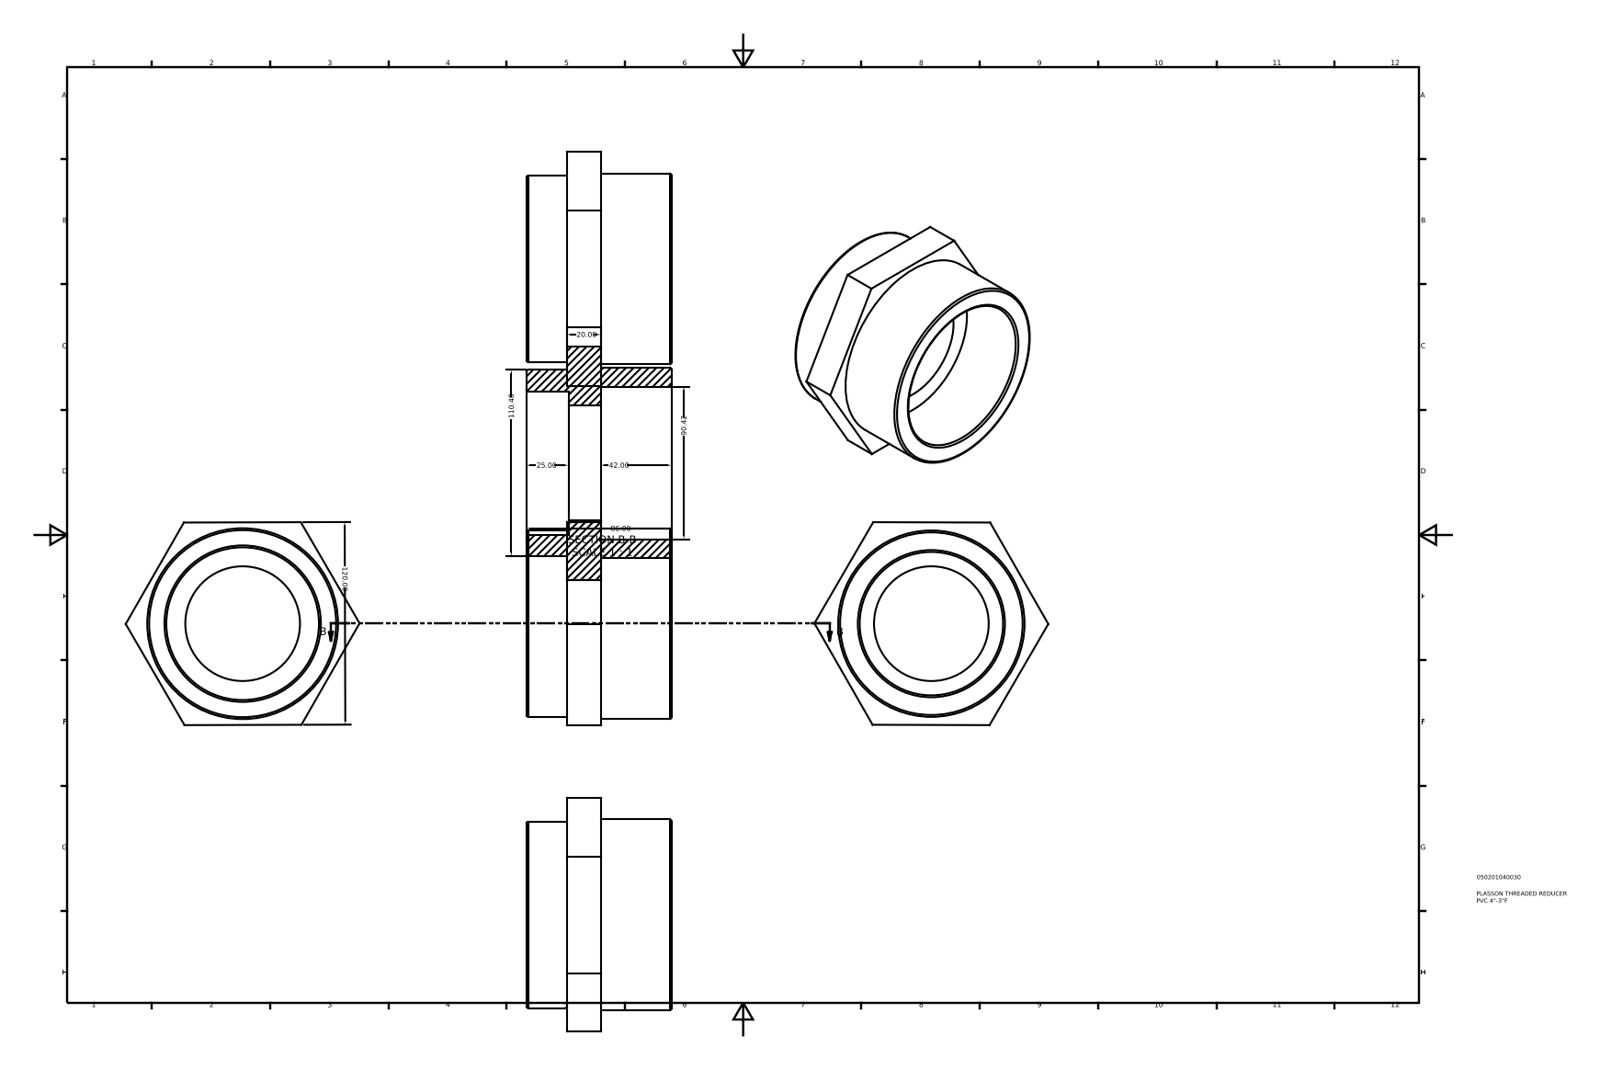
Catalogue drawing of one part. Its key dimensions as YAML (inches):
part_name: "050201040030"
step_written_by: "Autodesk Inventor 2015 (AUTOMOTIVE_DESIGN)"
units: inches
bodies: {solids: 1, faces: 21, planar: 12, cylindrical: 5, other: 4}
overall_size: [5.455, 4.732, 3.386]
volume: 25.63
surface_area: 110.5
round_holes:
  - {diameter: 2.675, count: 1}
  - {diameter: 3.344, count: 1}
  - {diameter: 3.56, count: 1}
round_bosses_or_shafts:
  - {diameter: 4.45, count: 1}
  - {diameter: 4.346, count: 1}
face_to_face_distances: [1.732, 0.945, 0.787, 3.386, 2.441, 1.654, 0.984, 0.039, 0.748, 2.402]
